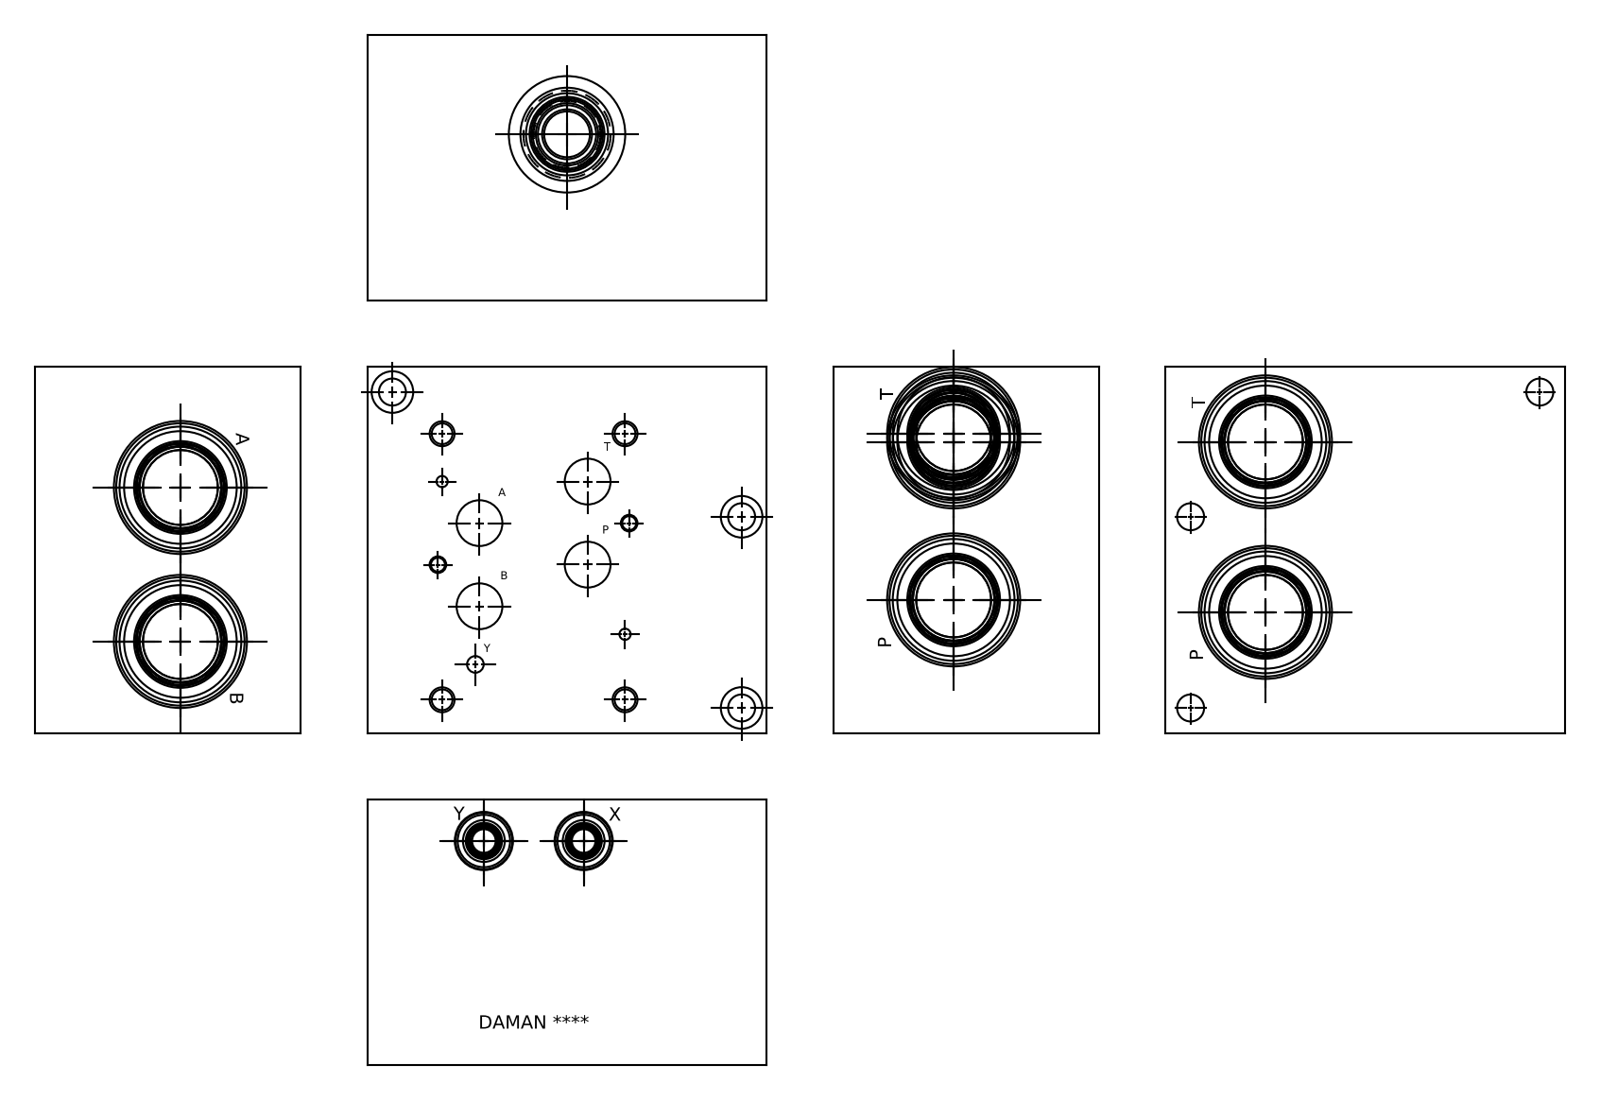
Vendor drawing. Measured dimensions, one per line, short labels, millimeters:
name: Part_AD07SPRVC16P_3D
written by: Autodesk Inventor 2020 (AUTOMOTIVE_DESIGN)
unit: mm
bodies: 1 solid, 610 faces (344 planar, 73 cylindrical, 193 other)
size: 152.4 × 139.7 × 101.6
volume: 1 868 000 mm³; area: 147 039 mm²
holes: 7× ⌀33.34, 6× ⌀28.57, 6× ⌀31.27, 6× ⌀33.76, 6× ⌀49.12, 4× ⌀5.11, 4× ⌀7.92, 4× ⌀9.53, 3× ⌀10.31, 3× ⌀15.88, 3× ⌀17.48, 2× ⌀4.37
face distances: 101.6, 139.7, 152.4, 0.79, 151.61, 150.82, 3.56, 98.04, 19.05, 138.91
hole spacings: 44.22, 22.45, 22.46, 31.75, 42.88, 57.15, 65.38, 69.85
